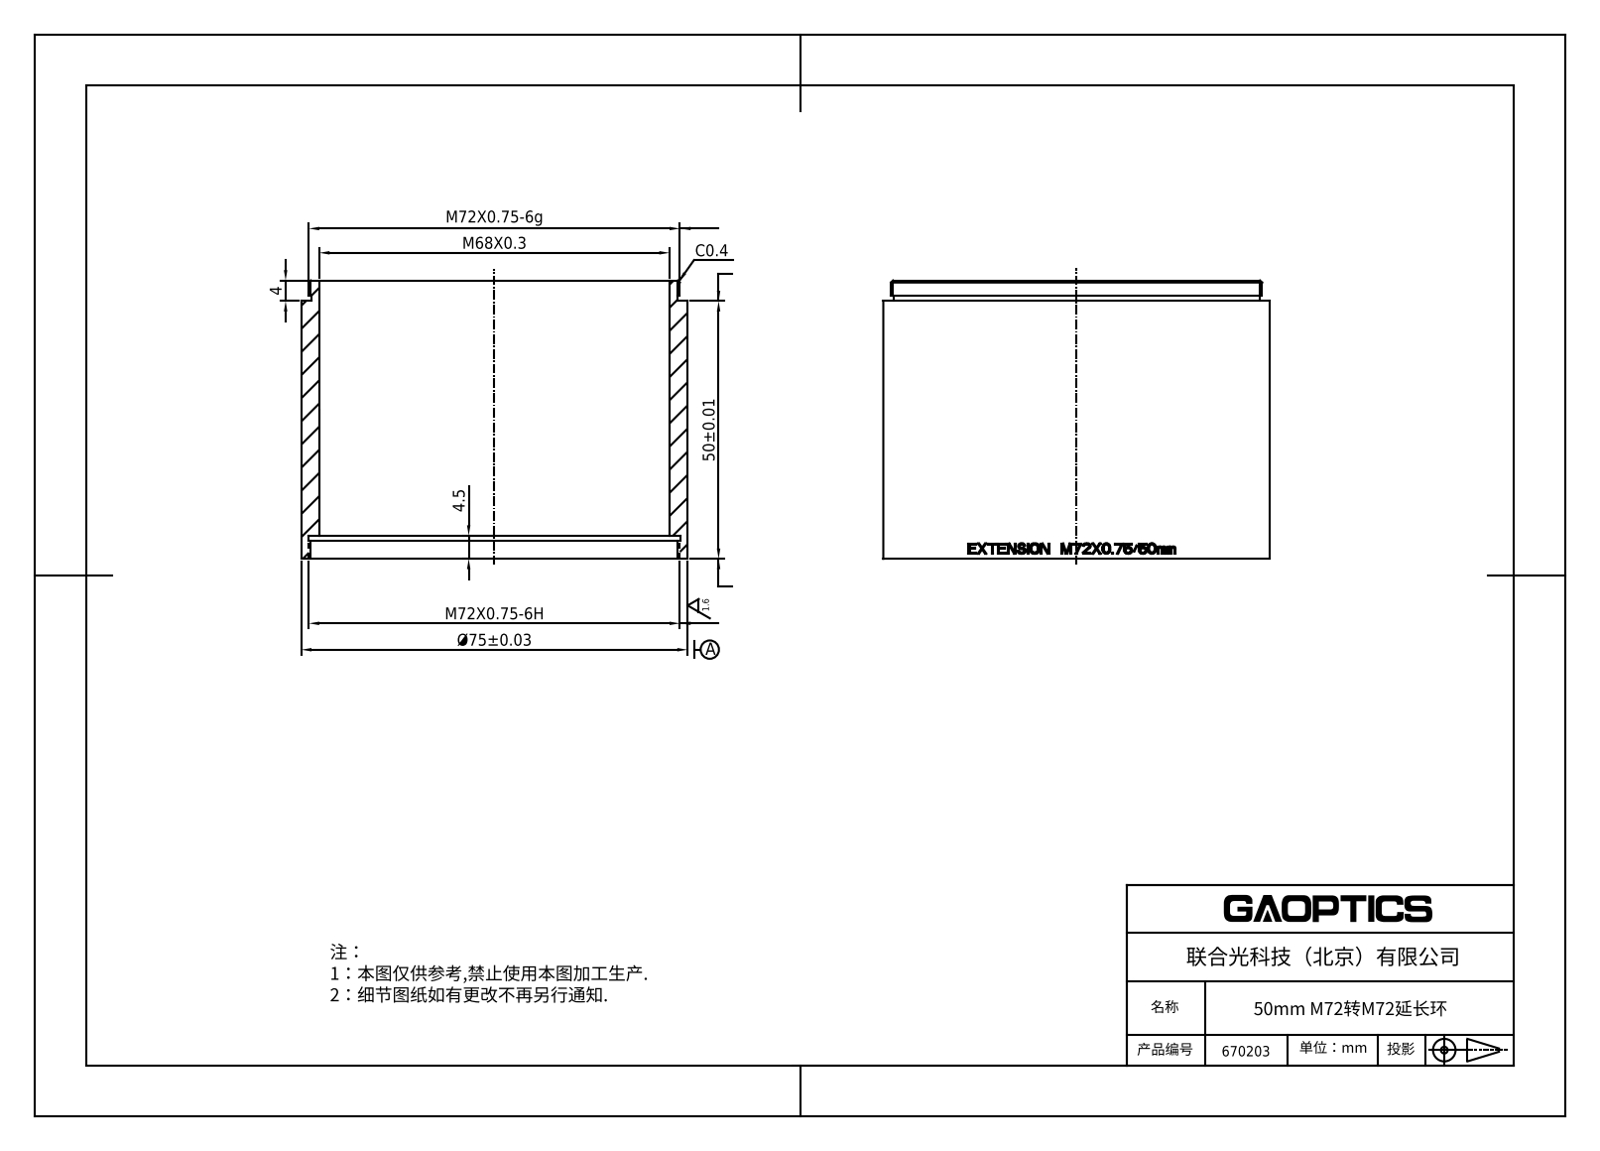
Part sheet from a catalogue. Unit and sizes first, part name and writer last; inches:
Units: inches
Overall size (bounding box): 2.953 × 2.953 × 2.126
Round holes (diameter × count): ⌀2.677 ×1, ⌀2.803 ×1, ⌀2.843 ×1
Round bosses / shafts (diameter × count): ⌀2.953 ×1, ⌀2.835 ×1, ⌀2.795 ×1
Main face-to-face distances: 1.791, 0.177, 1.969, 2.126, 1.949, 0.157, 0.039, 1.831, 0.138, 1.988
Volume: 2.385 in³ · Surface area: 41.16 in²
Bodies: 1 solid, 57 faces (6 planar, 45 cylindrical, 6 other)
Part name (STEP PRODUCT): 50mm
STEP written by: SolidWorks 2019 (CONFIG_CONTROL_DESIGN)
